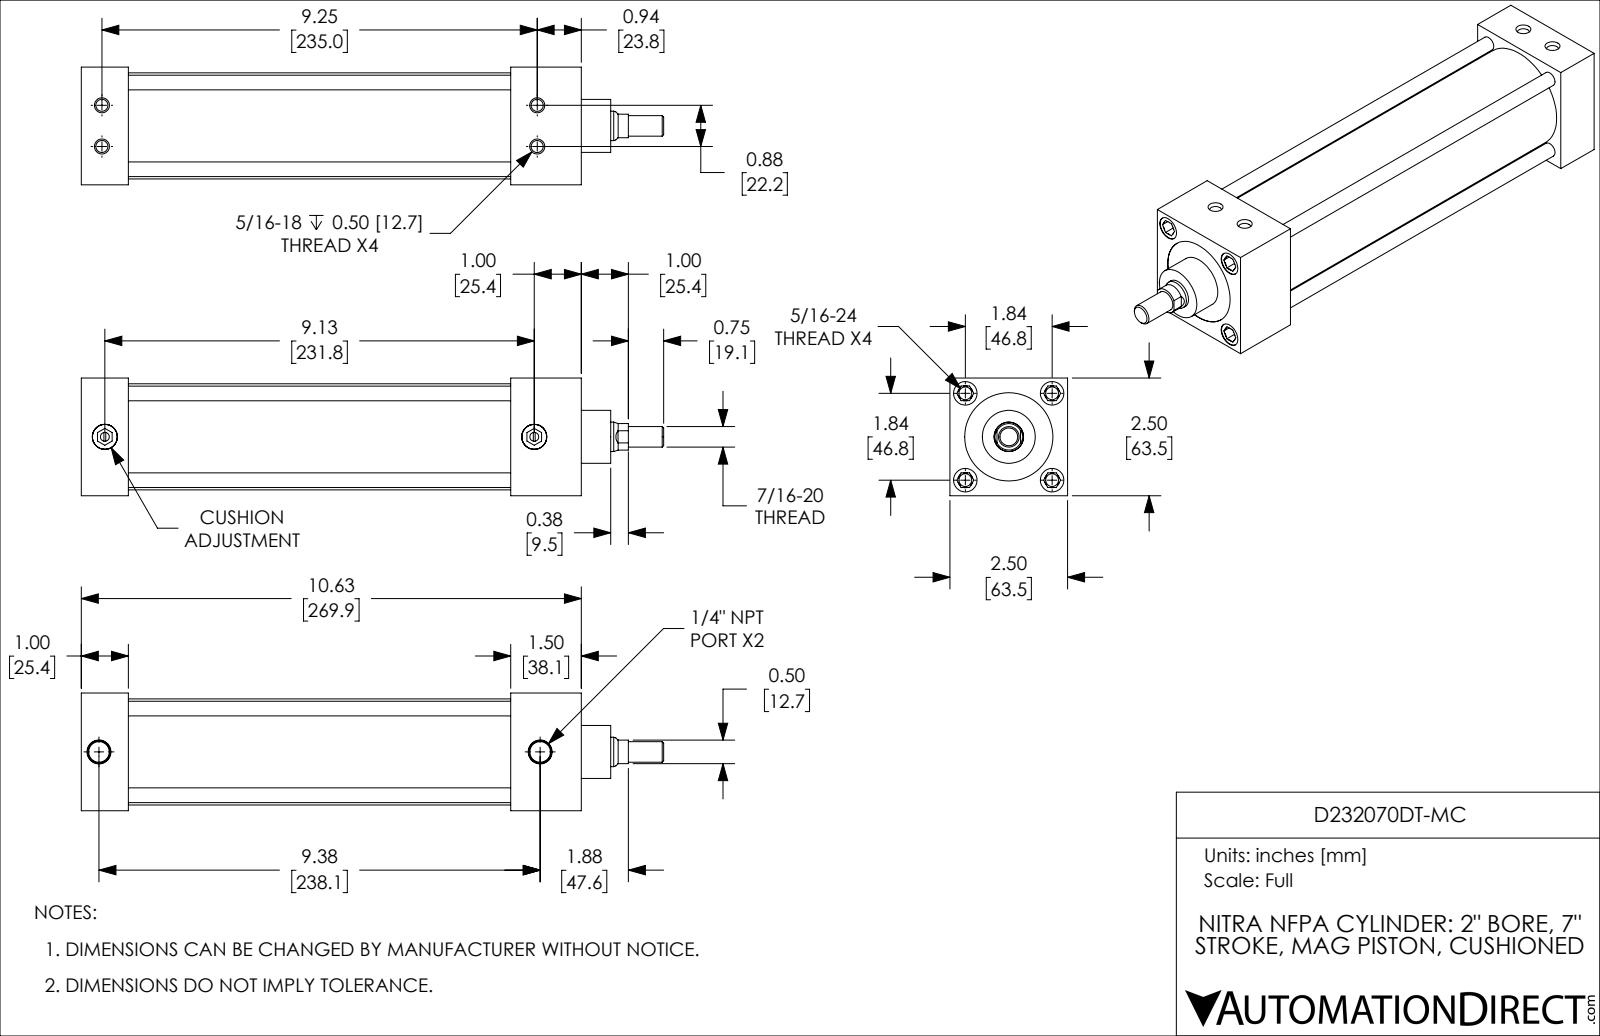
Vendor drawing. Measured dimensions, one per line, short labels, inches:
name: D232070DT-MC_PISTON_KK1; D232070DT-MC; D232070DT-MC_CUSHION; D232070DT-MC_BODY
written by: SolidWorks 2019 (CONFIG_CONTROL_DESIGN)
unit: in
bodies: 4 solids, 248 faces (90 planar, 78 cylindrical, 80 other)
size: 12.375 × 2.5 × 2.5
volume: 30.55 in³; area: 238.6 in²
holes: 7× ⌀0.272, 4× ⌀0.257, 4× ⌀0.5, 2× ⌀0.19, 2× ⌀0.438, 2× ⌀0.531, 1× ⌀0.626, 1× ⌀1.875, 1× ⌀2.001
bosses: 4× ⌀0.312, 2× ⌀0.532, 1× ⌀2.251, 1× ⌀1.999, 1× ⌀1.125, 1× ⌀0.624, 1× ⌀0.437
rounds: 1× R0.281
face distances: 2.5, 1, 9.125, 8.125, 1.125, 2.125, 7, 10.625, 9.625, 8.5
hole spacings: 1.84, 1.844, 1.301, 0.441, 0.443, 0.875, 1.304, 2.602
